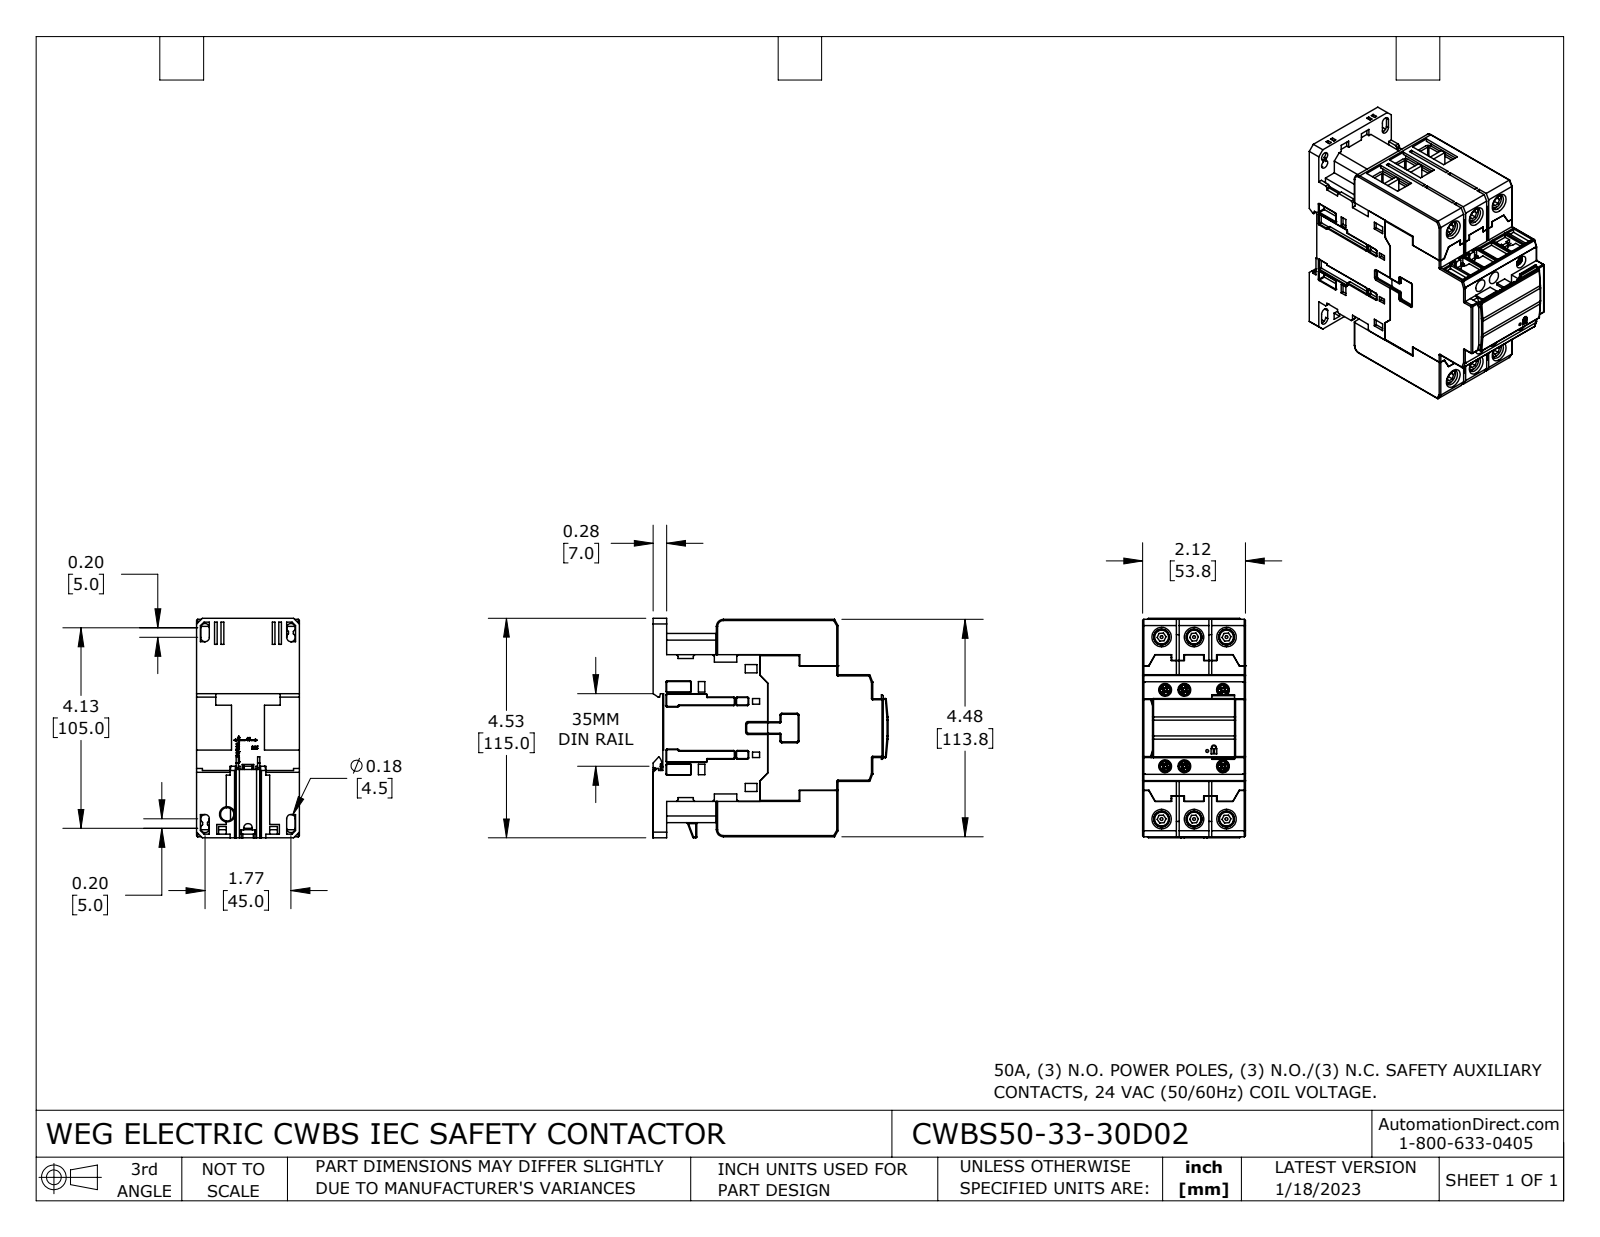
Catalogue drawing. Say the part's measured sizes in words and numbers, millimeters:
The part is named "CWBS50-33-30D02". Its 3-D file was written by "SolidWorks 2021 (CONFIG_CONTROL_DESIGN)". It is 37 solids with 2637 faces: 1669 planar, 550 cylindrical and 418 other. Overall it measures 123.1 by 115 by 53.8 millimeters. Its volume is 551 800 cubic millimeters and its surface area 135 000 square millimeters. Round holes: 6 of diameter 3.1, 6 of diameter 5, 6 of diameter 6.7, 6 of diameter 8.2, 4 of diameter 4.5, 2 of diameter 3.2, 2 of diameter 7, 1 of diameter 1.5. Round bosses or shafts: 6 of diameter 8.7, 6 of diameter 6, 6 of diameter 3.4. Partial cylindrical surfaces (rounded edges, fillets, slot ends): 89 of radius 0.5, 69 of radius 0.3, 48 of radius 0.1, 42 of radius 0.6, 18 of radius 2, 5 of radius 2.3, 3 of radius 1, 3 of radius 1.5. The main face-to-face distances are 1.5, 53.8, 17, 18.5, 76.8, 95.3, 2.7, 5.5, 96.8, 2.5. The hole center spacings are 17, 27.7, 31.5, 42.4, 67.7, 69.3, 74.9, 96.8.
